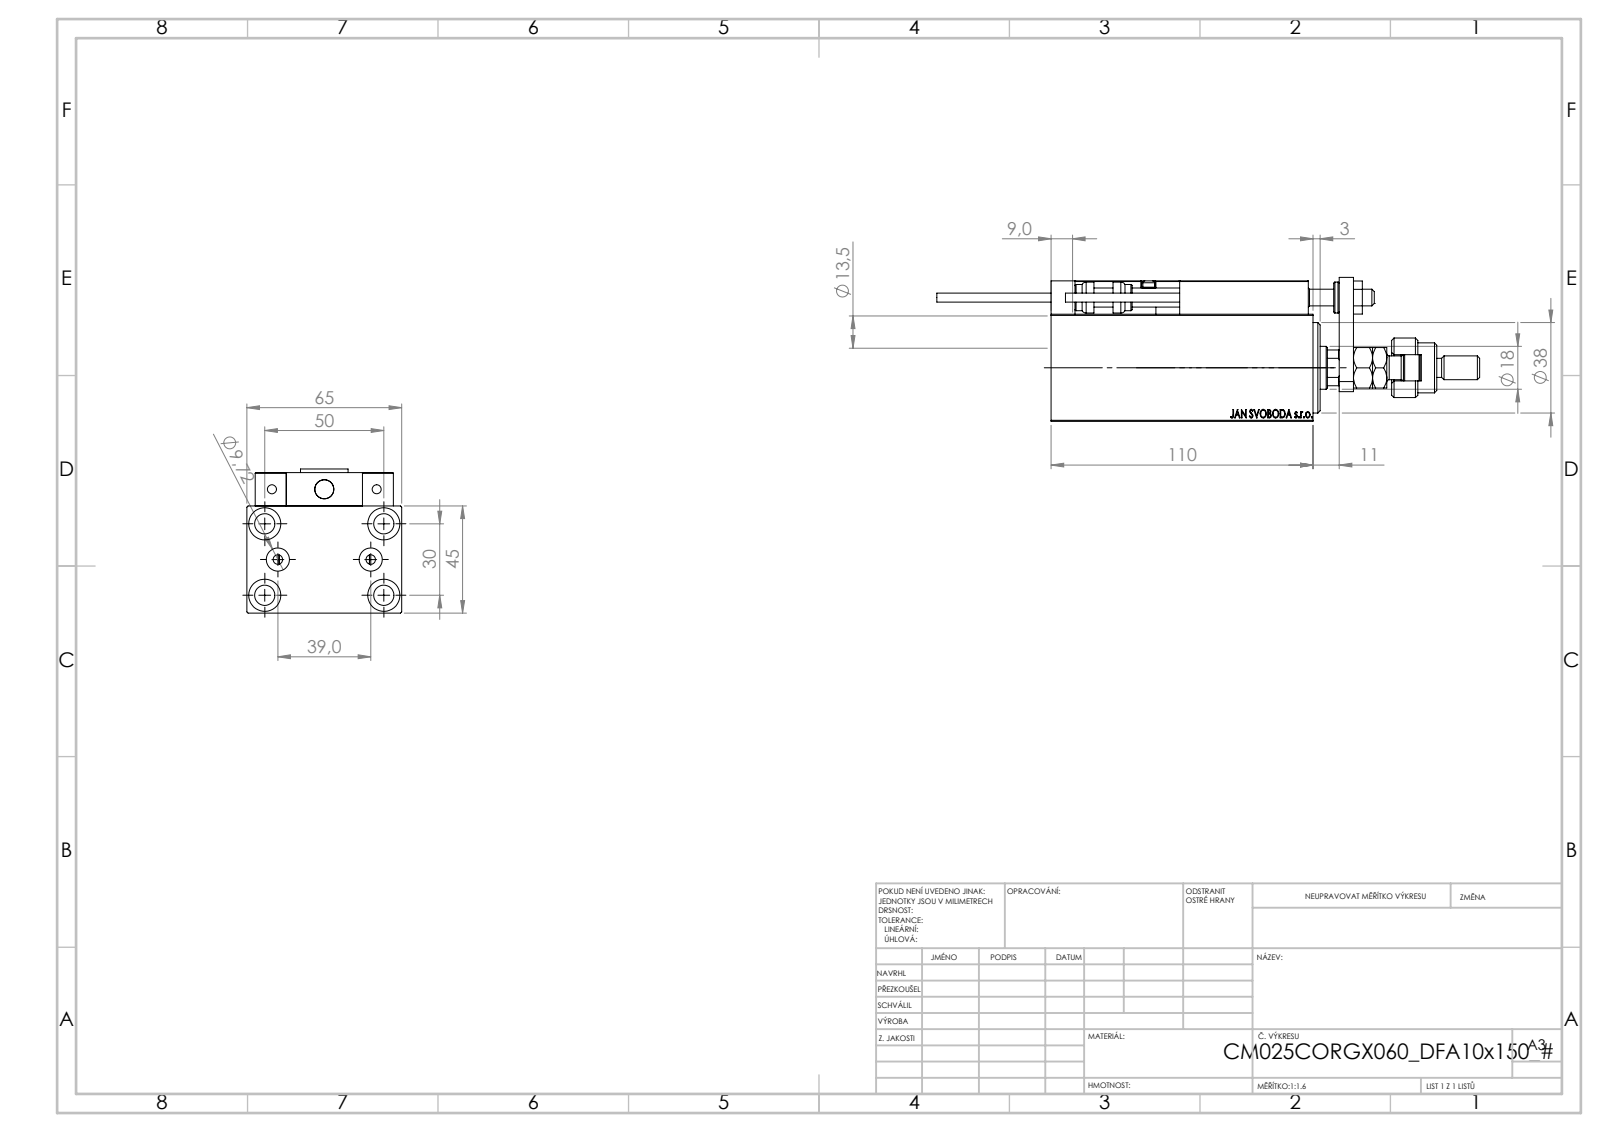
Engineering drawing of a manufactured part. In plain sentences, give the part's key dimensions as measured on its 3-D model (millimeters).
The part is named "V450CM_C_VCP; MAGNET; ALLEN BOLT D5; MFA (+8 more)". Its 3-D file was written by "SolidWorks 2019 (CONFIG_CONTROL_DESIGN)". It is 25 solids with 1363 faces: 588 planar, 197 cylindrical and 578 other. Overall it measures 228 by 65 by 60.5 millimeters. Its volume is 335 238 cubic millimeters and its surface area 92 735 square millimeters. Round holes: 6 of diameter 4, 5 of diameter 8, 5 of diameter 8.5, 4 of diameter 3.2, 4 of diameter 13.5, 2 of diameter 5, 2 of diameter 9.72, 1 of diameter 7, 1 of diameter 14.5, 1 of diameter 18, 1 of diameter 21.5, 1 of diameter 27. Round bosses or shafts: 2 of diameter 5, 2 of diameter 3.8, 1 of diameter 25, 1 of diameter 21, 1 of diameter 16, 1 of diameter 13, 1 of diameter 11, 1 of diameter 10. Partial cylindrical surfaces (rounded edges, fillets, slot ends): 30 of radius 0.3, 2 of radius 3, 1 of radius 5.5, 1 of radius 8.5, 1 of radius 8.75. The main face-to-face distances are 45, 65, 14, 59, 5, 13, 25, 7, 3, 19. The hole center spacings are 15.98, 29.15, 46.96, 11.37, 19.5, 20, 28.9, 29.59.
